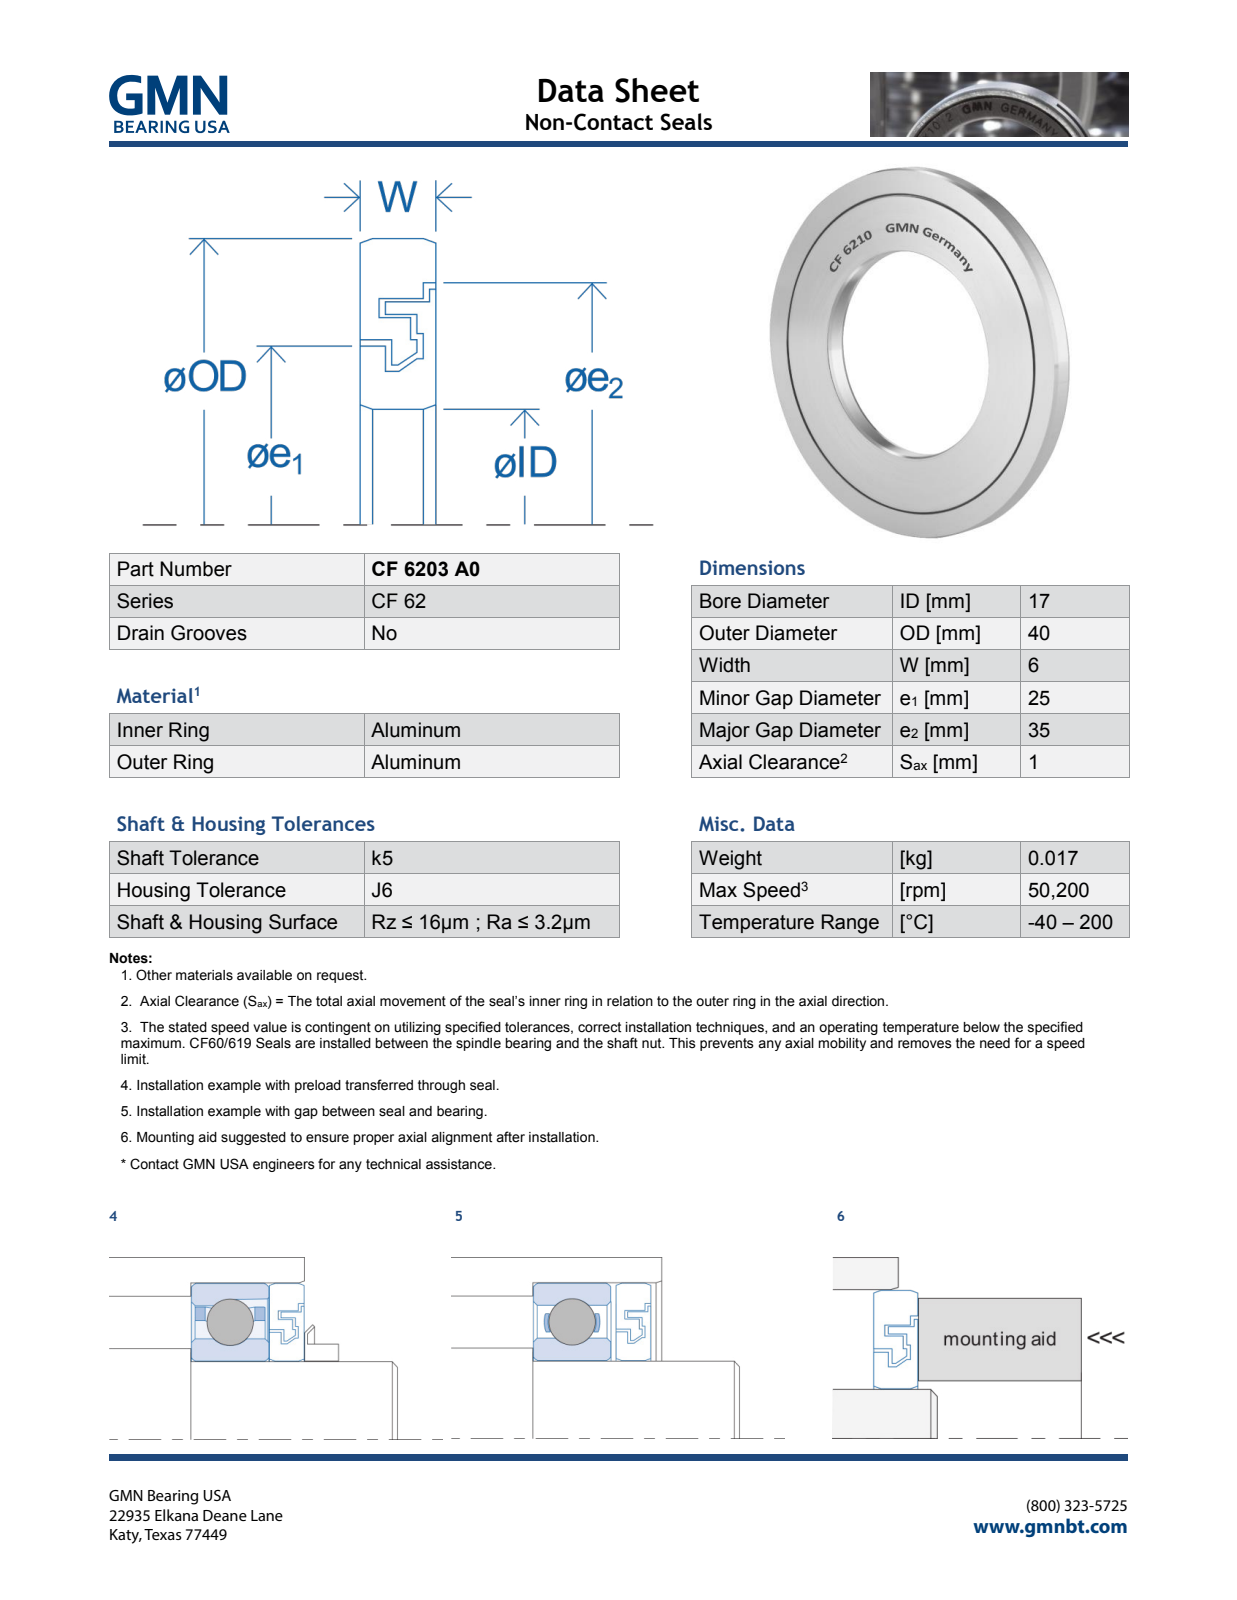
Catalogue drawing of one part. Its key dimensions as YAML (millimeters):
part_name: "CF6203A0_PRT"
step_written_by: "PRO/ENGINEER BY PARAMETRIC TECHNOLOGY CORPORATION, 2013150 (AUTOMOTIVE_DESIGN)"
units: millimeters
bodies: {solids: 2, faces: 636, planar: 594, cylindrical: 30, other: 12}
overall_size: [40, 40, 6.05]
volume: 5403
surface_area: 6417
round_holes:
  - {diameter: 17, count: 1}
  - {diameter: 22, count: 1}
  - {diameter: 26, count: 1}
  - {diameter: 27, count: 1}
  - {diameter: 30, count: 1}
  - {diameter: 32.5, count: 1}
  - {diameter: 35, count: 1}
round_bosses_or_shafts:
  - {diameter: 40, count: 1}
  - {diameter: 34, count: 1}
  - {diameter: 32, count: 1}
  - {diameter: 29.5, count: 1}
  - {diameter: 25, count: 1}
  - {diameter: 23, count: 1}
  - {diameter: 21, count: 1}
face_to_face_distances: [6, 0.5, 2, 1, 2.5, 1.5, 4, 3, 3.5, 4.5]
